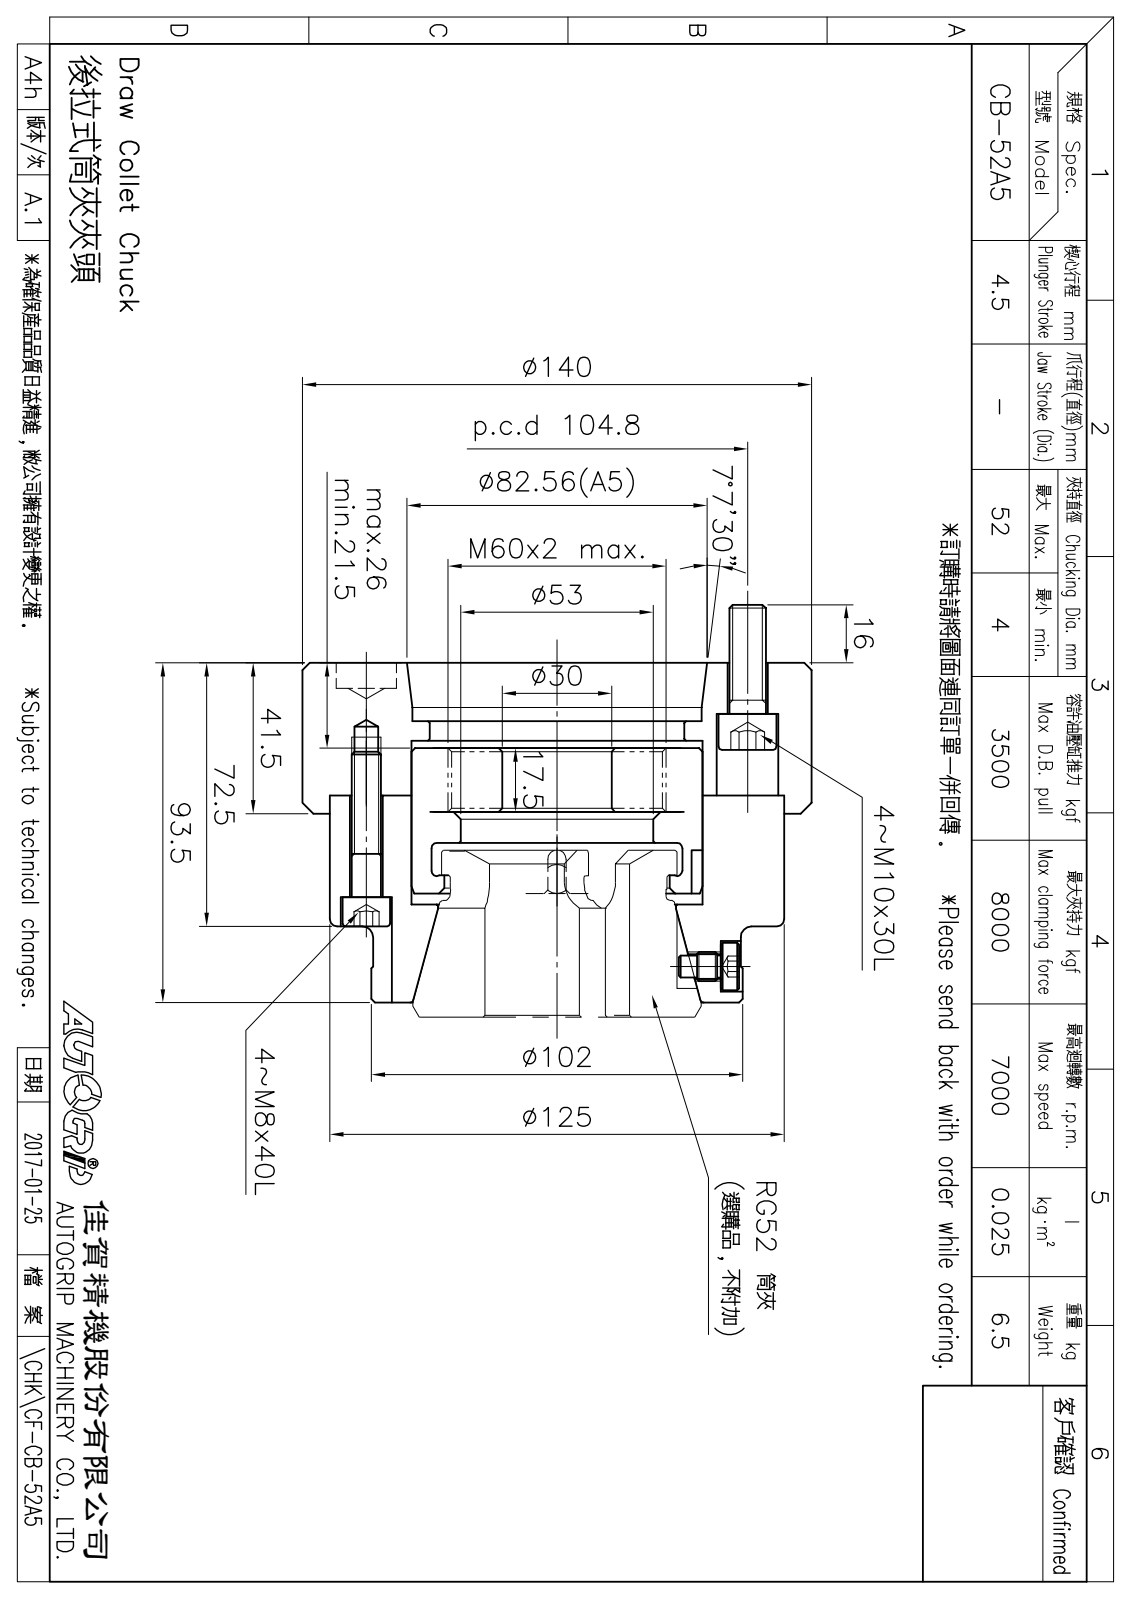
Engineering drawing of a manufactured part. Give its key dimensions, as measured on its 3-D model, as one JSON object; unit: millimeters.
{"part_name": "CF-CB-52A5; 圓頭內六角螺栓_M8x40; CF-CB-52-01000; CF-CB-52-02000 (+2 more)", "step_written_by": "SolidWorks 2016 (CONFIG_CONTROL_DESIGN)", "units": "millimeters", "bodies": {"solids": 11, "faces": 371, "planar": 145, "cylindrical": 116, "other": 110}, "overall_size": [140, 140, 109.5], "volume_mm3": 844855, "surface_area_mm2": 153453, "round_holes": [[6.8, 5], [14, 5], [9, 4], [11, 4], [17, 4], [16.5, 2], [30, 1], [53, 1], [62, 1], [65.5, 1], [69, 1], [70, 1]], "round_bosses_or_shafts": [[16, 4], [13, 4], [10, 4], [8, 4], [140, 1], [102, 1], [101, 1]], "face_to_face_distances": [36.5, 15, 25, 21.5, 20, 5, 2.5, 6, 72.5, 11], "hole_center_spacings": [52.4, 40.1, 74.1, 96.82, 104.8, 13.68, 27.12, 63.8]}
